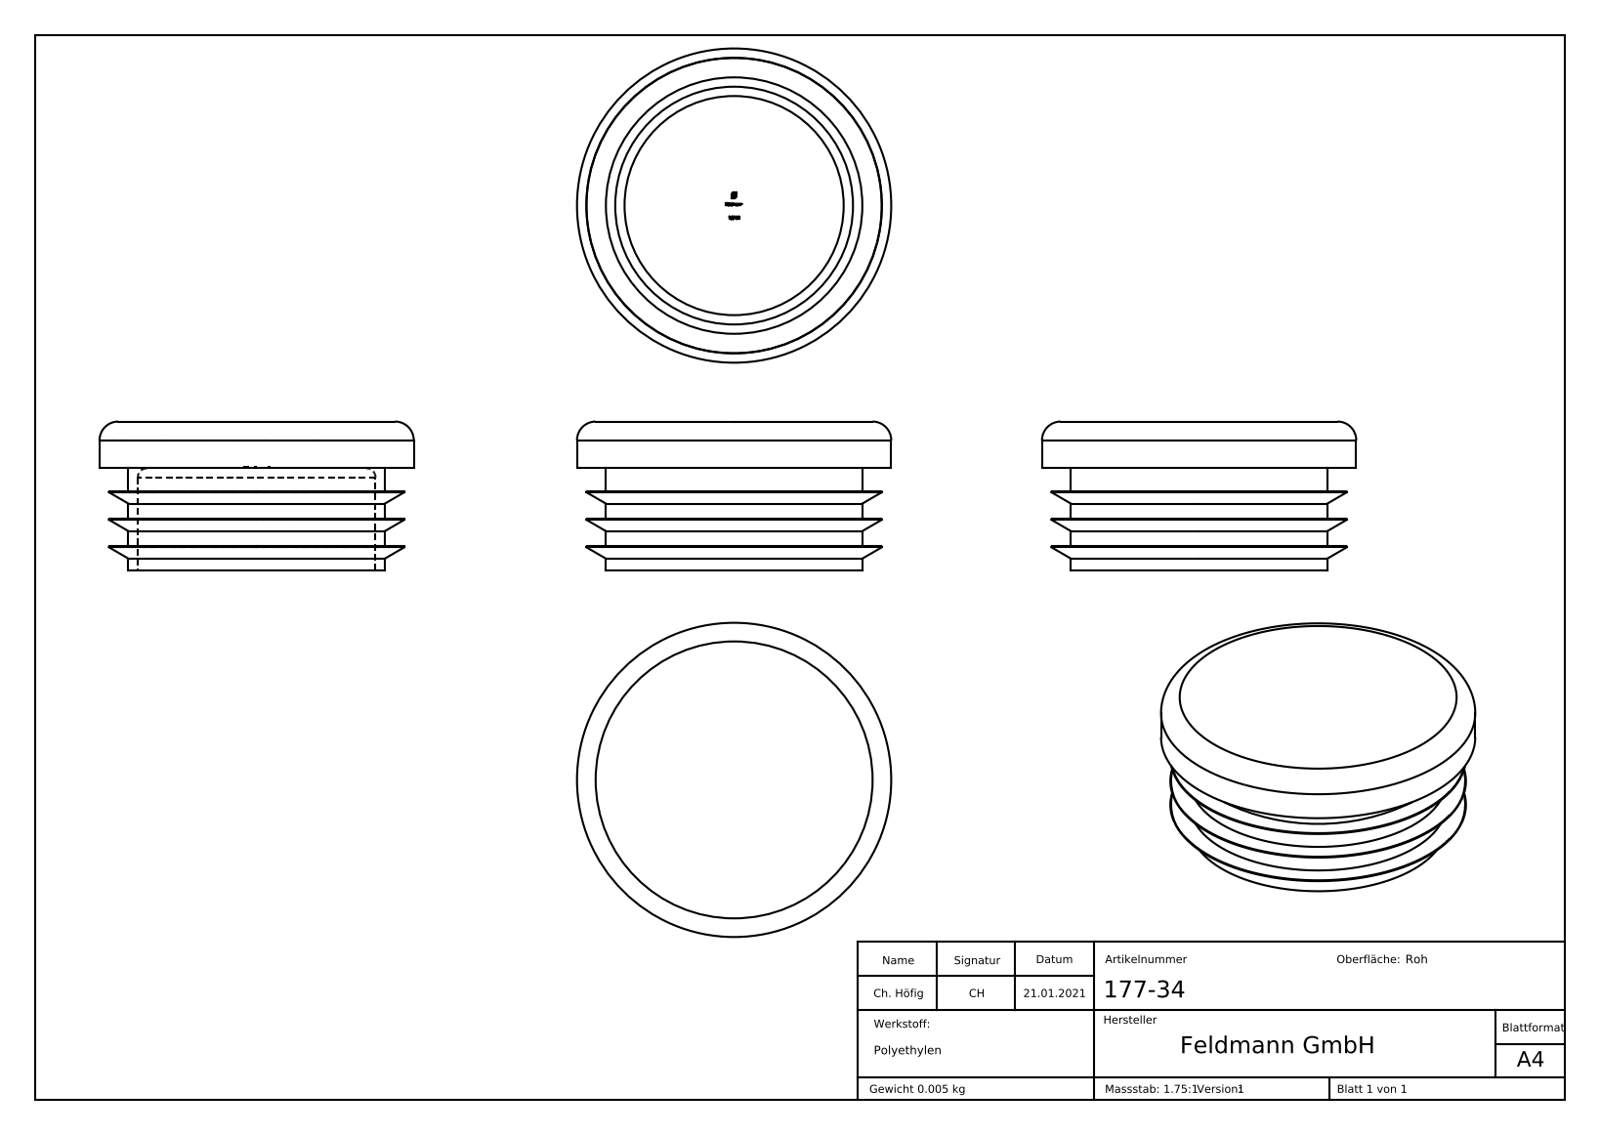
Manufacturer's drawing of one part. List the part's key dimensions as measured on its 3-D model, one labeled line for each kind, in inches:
Part name (STEP PRODUCT): 177-34
STEP written by: SolidWorks 2015 (CONFIG_CONTROL_DESIGN)
Units: inches
Bodies: 1 solid, 199 faces (117 planar, 12 cylindrical, 70 other)
Overall size (bounding box): 1.327 × 1.327 × 0.65
Volume: 0.333 in³ · Surface area: 8.336 in²
Round holes (diameter × count): ⌀0.972 ×1
Round bosses / shafts (diameter × count): ⌀1.327 ×1, ⌀1.051 ×1
Main face-to-face distances: 0.197, 0.118, 0.236, 0.354, 0.551, 0.433, 0.315, 0.098, 0.217, 0.335
